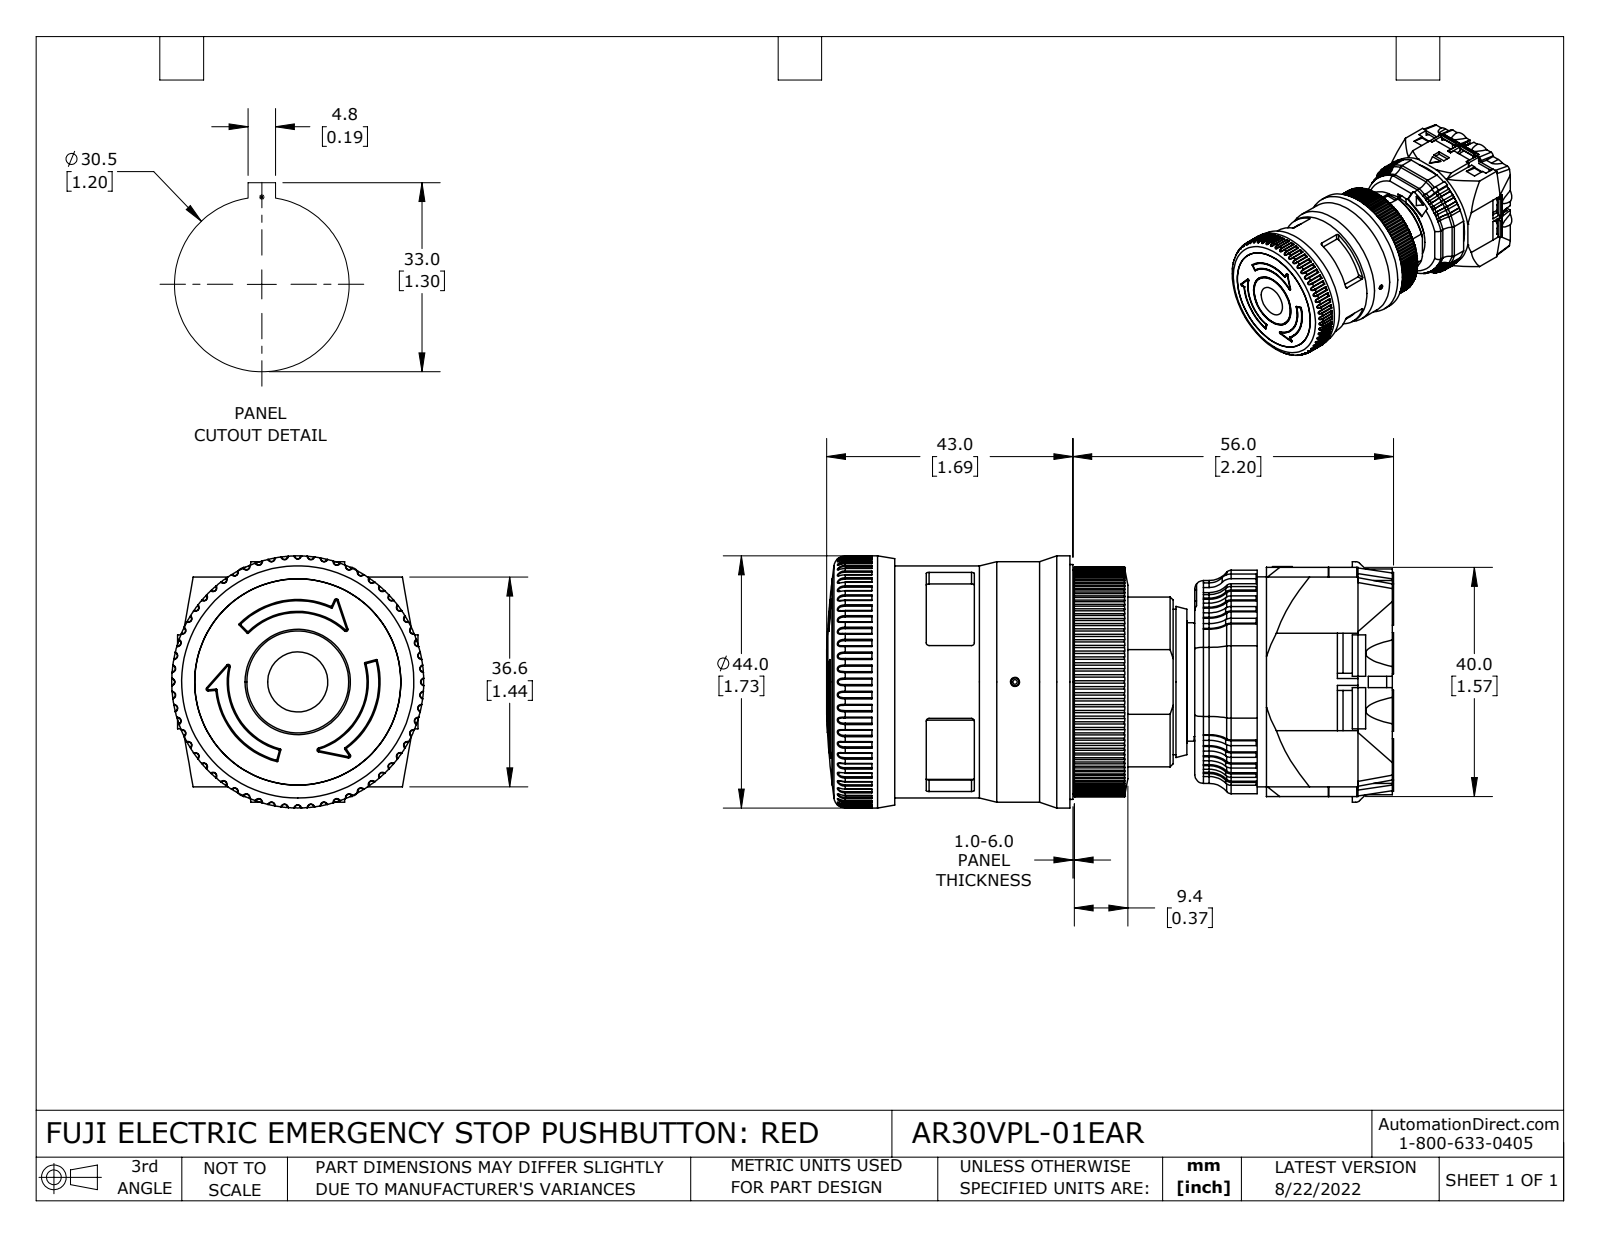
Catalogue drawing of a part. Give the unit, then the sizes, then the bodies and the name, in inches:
Units: inches
Overall size (bounding box): 3.898 × 1.732 × 1.732
Round holes (diameter × count): ⌀0.138 ×12, ⌀0.244 ×12, ⌀0.13 ×2, ⌀0.031 ×1, ⌀0.063 ×1, ⌀0.26 ×1, ⌀0.315 ×1, ⌀0.689 ×1, ⌀0.693 ×1, ⌀0.724 ×1, ⌀0.827 ×1, ⌀0.843 ×1
Round bosses / shafts (diameter × count): ⌀0.283 ×12, ⌀1.732 ×1, ⌀1.654 ×1, ⌀1.614 ×1, ⌀1.535 ×1, ⌀1.417 ×1, ⌀1.299 ×1, ⌀1.291 ×1
Partial cylindrical surfaces — rounded edges, fillets, slot ends (radius × count): R0.008 ×120, R0.013 ×120, R0.02 ×76, R0.005 ×24, R0.049 ×19, R0.148 ×19, R0.039 ×15, R0.059 ×12
Main face-to-face distances: 0.118, 1.48, 0.039, 0.839, 1.598, 0.102, 1.516, 1.496, 1.378, 0.339
Hole centre spacings: 0.641, 0.907, 0.325, 0.349, 0.394, 0.585, 0.713, 0.735
Volume: 6.151 in³ · Surface area: 109.1 in²
Bodies: 32 solids, 2480 faces (1039 planar, 1119 cylindrical, 322 other)
Part name (STEP PRODUCT): AR30VPL-01EAR
STEP written by: SolidWorks 2021 (CONFIG_CONTROL_DESIGN)
